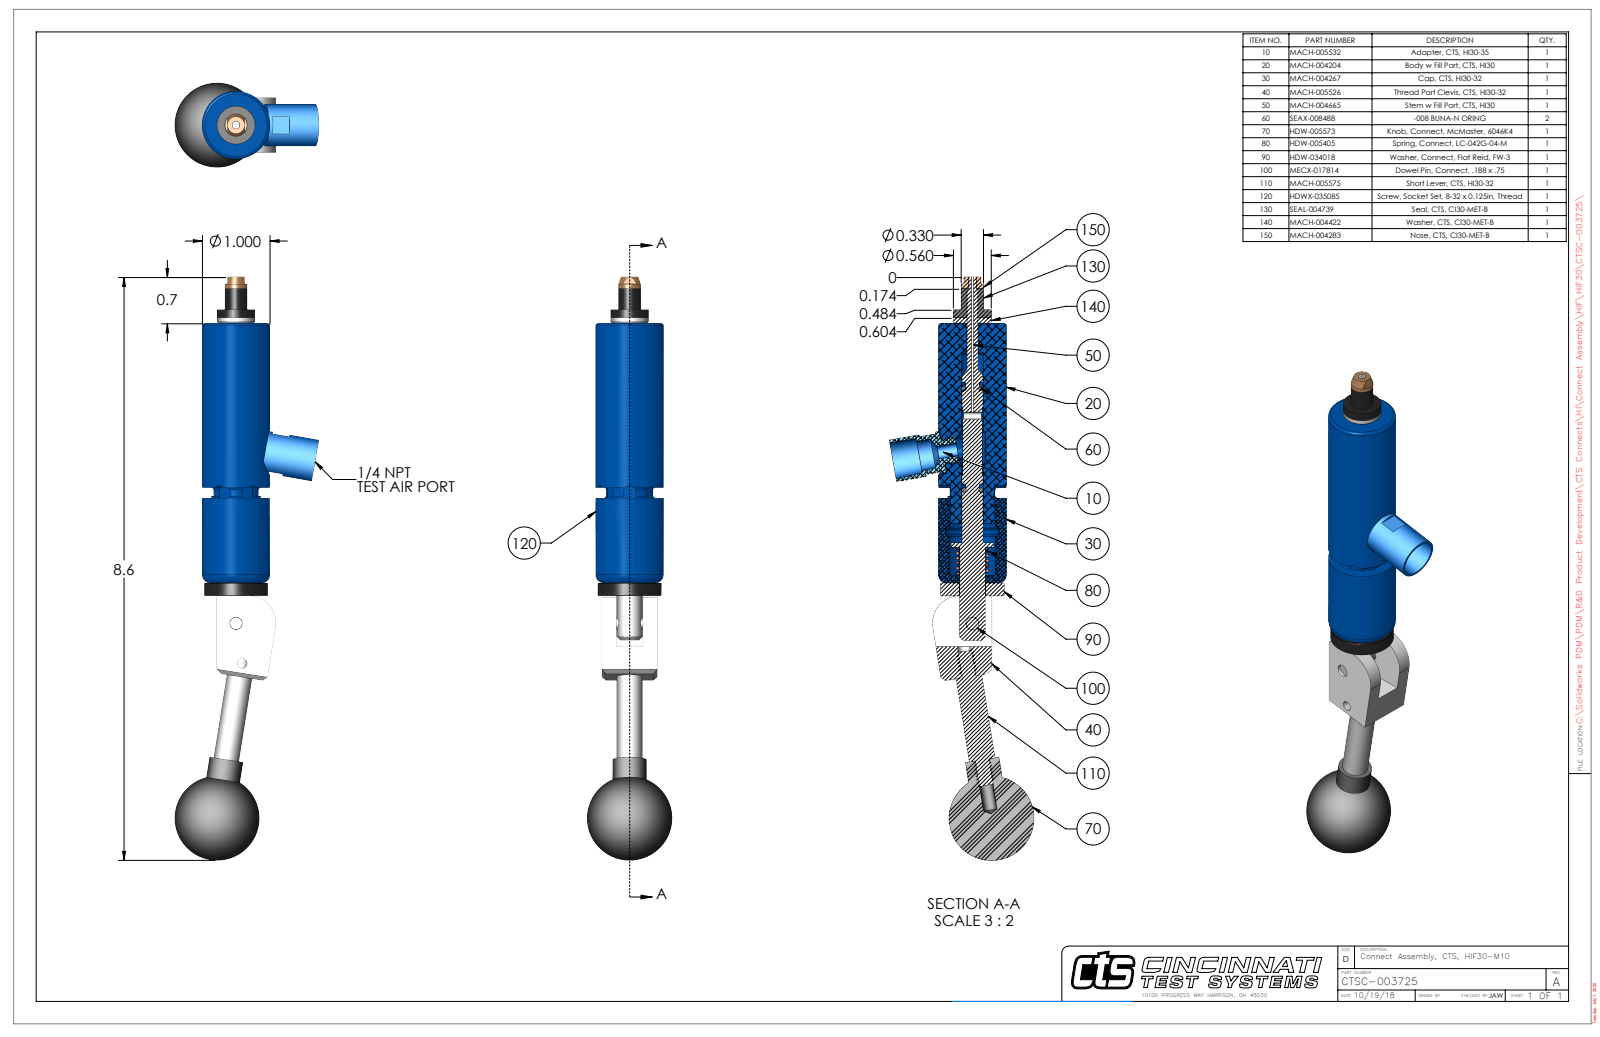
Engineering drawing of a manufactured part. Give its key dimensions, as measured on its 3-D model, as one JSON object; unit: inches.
{"part_name": "CTSC-003725", "step_written_by": "SolidWorks 2023 (AUTOMOTIVE_DESIGN)", "units": "inches", "bodies": {"solids": 10, "faces": 304, "planar": 117, "cylindrical": 122, "other": 65}, "overall_size": [8.618, 2.128, 1.25], "volume_in3": 5.043, "surface_area_in2": 37.58, "round_holes": [[0.201, 2], [0.04, 1], [0.09, 1], [0.113, 1], [0.136, 1], [0.15, 1], [0.155, 1], [0.161, 1], [0.164, 1], [0.187, 1], [0.189, 1], [0.385, 1]], "round_bosses_or_shafts": [[1, 1], [0.936, 1], [0.62, 1], [0.56, 1], [0.5, 1], [0.38, 1], [0.375, 1], [0.33, 1]], "partial_cylinders_radius": [[0.093, 6], [0.015, 1], [0.054, 1], [0.325, 1], [0.375, 1], [0.4, 1], [0.449, 1], [0.48, 1]], "face_to_face_distances": [0.21, 0.602, 0.812, 3.837, 4.024, 0.187, 0.391, 0.08, 3.917, 4.104], "hole_center_spacings": [0.599, 1.658, 2.252]}
